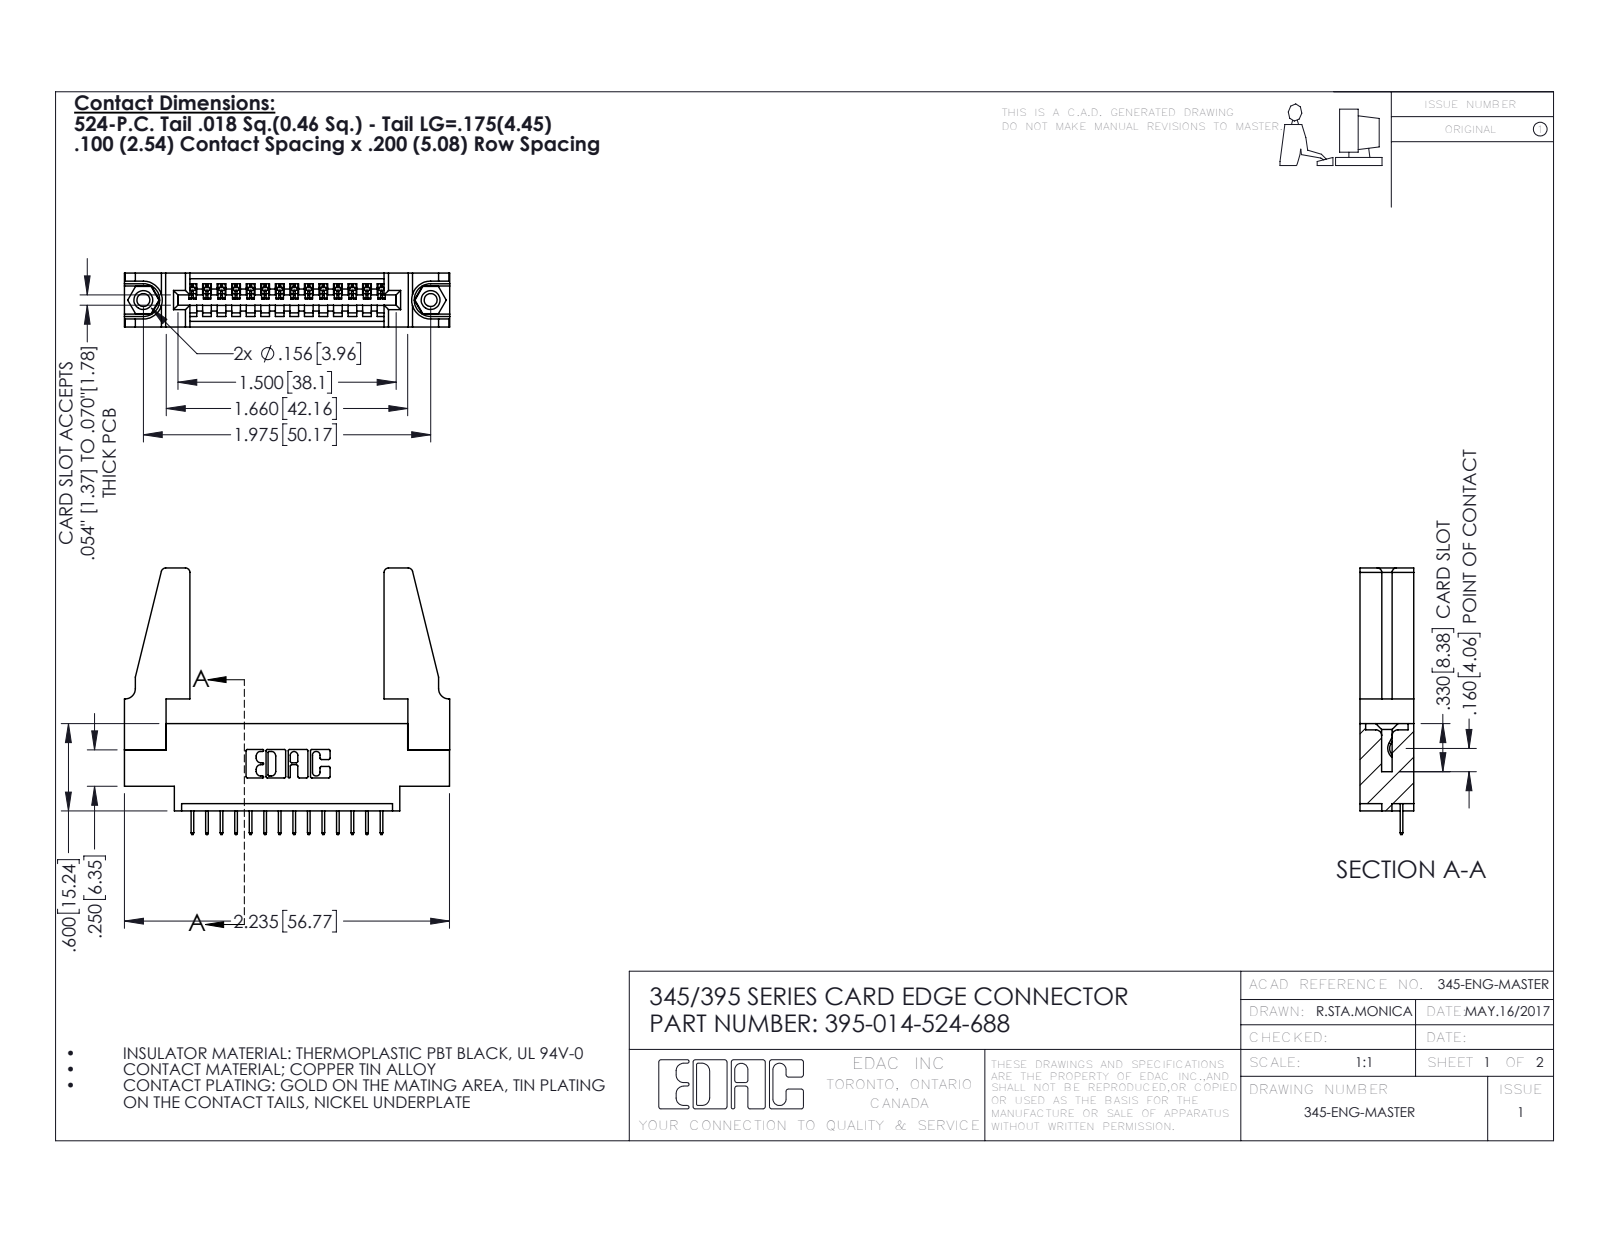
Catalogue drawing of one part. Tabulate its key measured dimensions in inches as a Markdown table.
| quantity | value |
| --- | --- |
| part name | 345-220-078_345-220-088; 395-014-524-688; 345-250-001_345-250-001-102; 345-292-001_345-293-124 (+1 more) |
| STEP written by | SolidWorks 2016 (CONFIG_CONTROL_DESIGN) |
| units | inches |
| bodies | 19 solids, 1122 faces (800 planar, 306 cylindrical, 16 other) |
| overall size | 2.236 × 1.832 × 0.37 |
| volume | 0.503 in³ |
| surface area | 14.47 in² |
| round holes (diameter × count) | 0.089 × 2, 0.125 × 2, 0.156 × 2, 0.064 × 1 |
| round bosses / shafts (diameter × count) | 0.155 × 2 |
| partial cylindrical surfaces (radius × count) | 0.006 × 28, 0.01 × 22, 0.03 × 8, 0.007 × 6, 0.031 × 6, 0.026 × 3, 0.031 × 2, 0.04 × 2 |
| main face-to-face distances | 0.37, 0.072, 0.298, 0.2, 0.098, 0.272, 0.025, 0.225, 0.148, 0.15 |
| hole center spacings | 0.27, 1.742, 1.975 |
